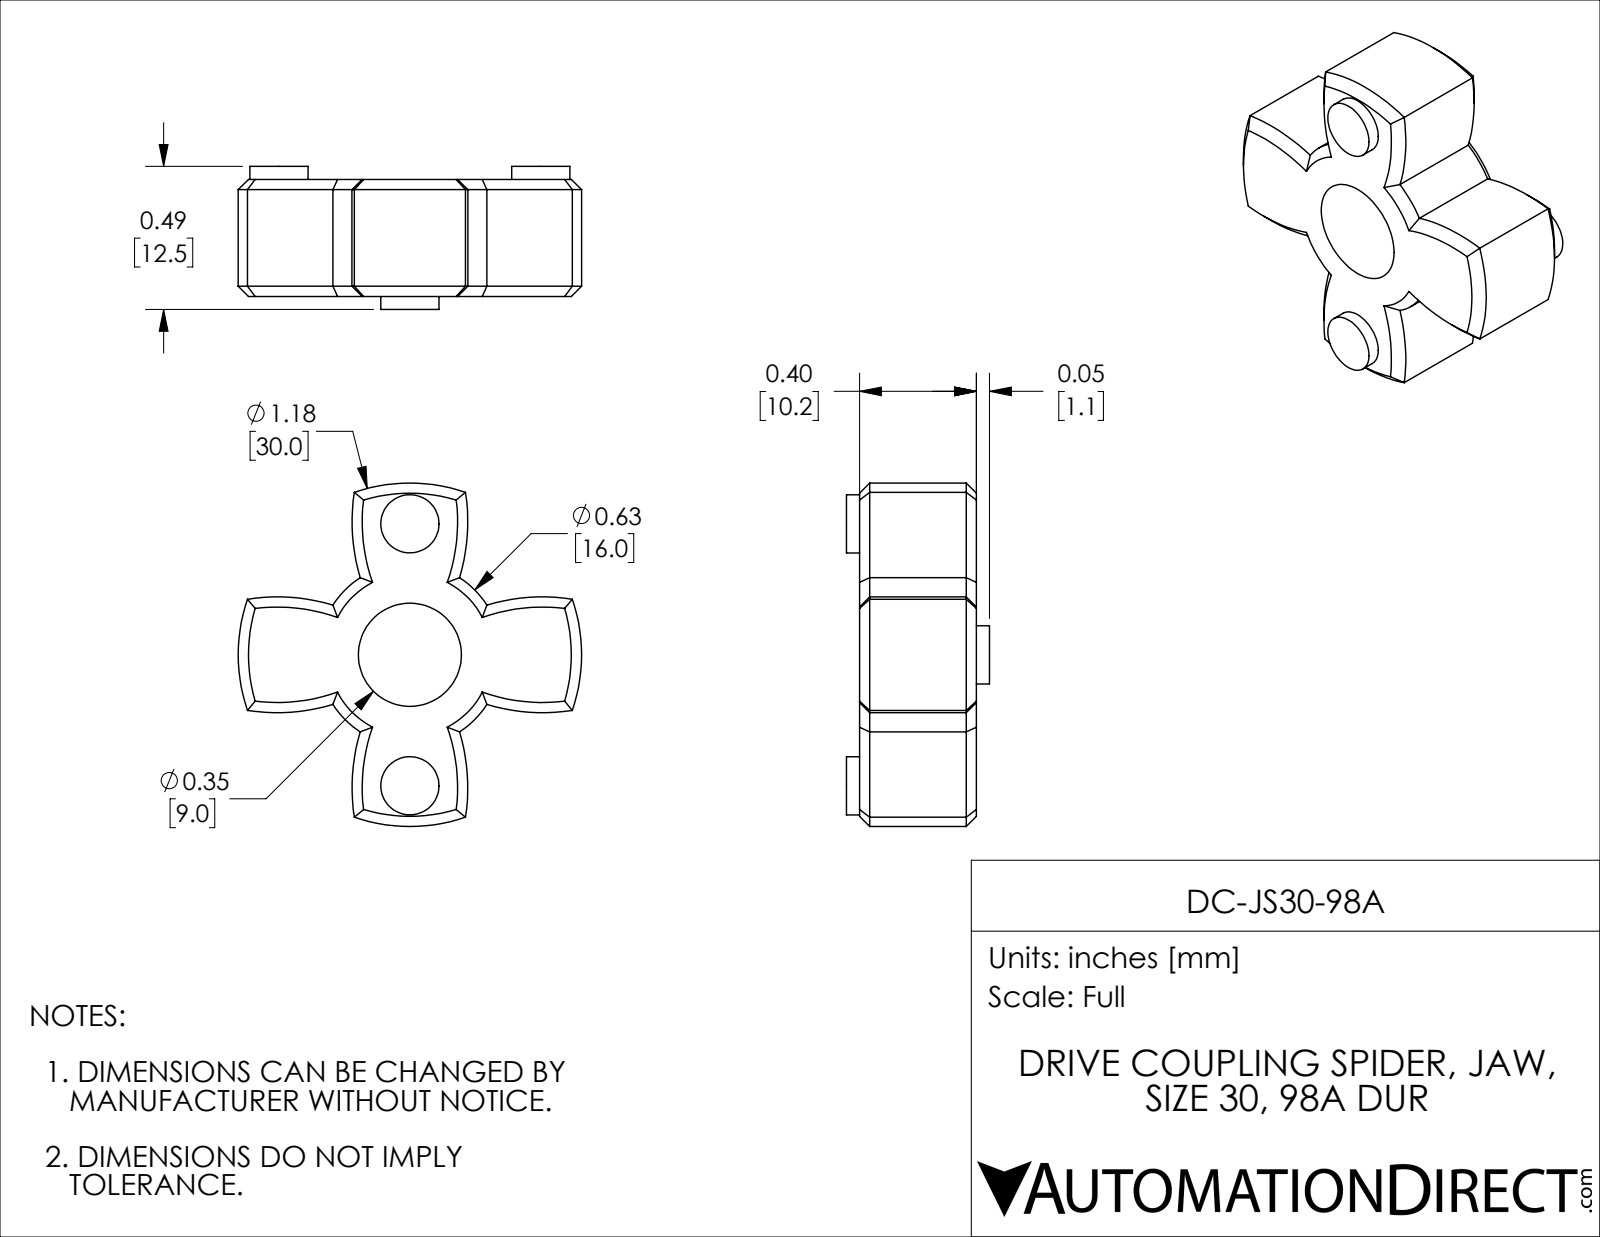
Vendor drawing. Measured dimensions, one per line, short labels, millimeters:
name: DC-JS30-98A
written by: SolidWorks 2019 (AUTOMOTIVE_DESIGN)
unit: mm
bodies: 1 solid, 73 faces (6 planar, 29 cylindrical, 38 other)
size: 29.97 × 29.97 × 12.5
volume: 4 285 mm³; area: 2 239 mm²
holes: 1× ⌀9
bosses: 4× ⌀5.08
rounds: 4× R16.64, 1× R8, 1× R14.99
face distances: 10.22, 1.14, 11.36, 12.5
